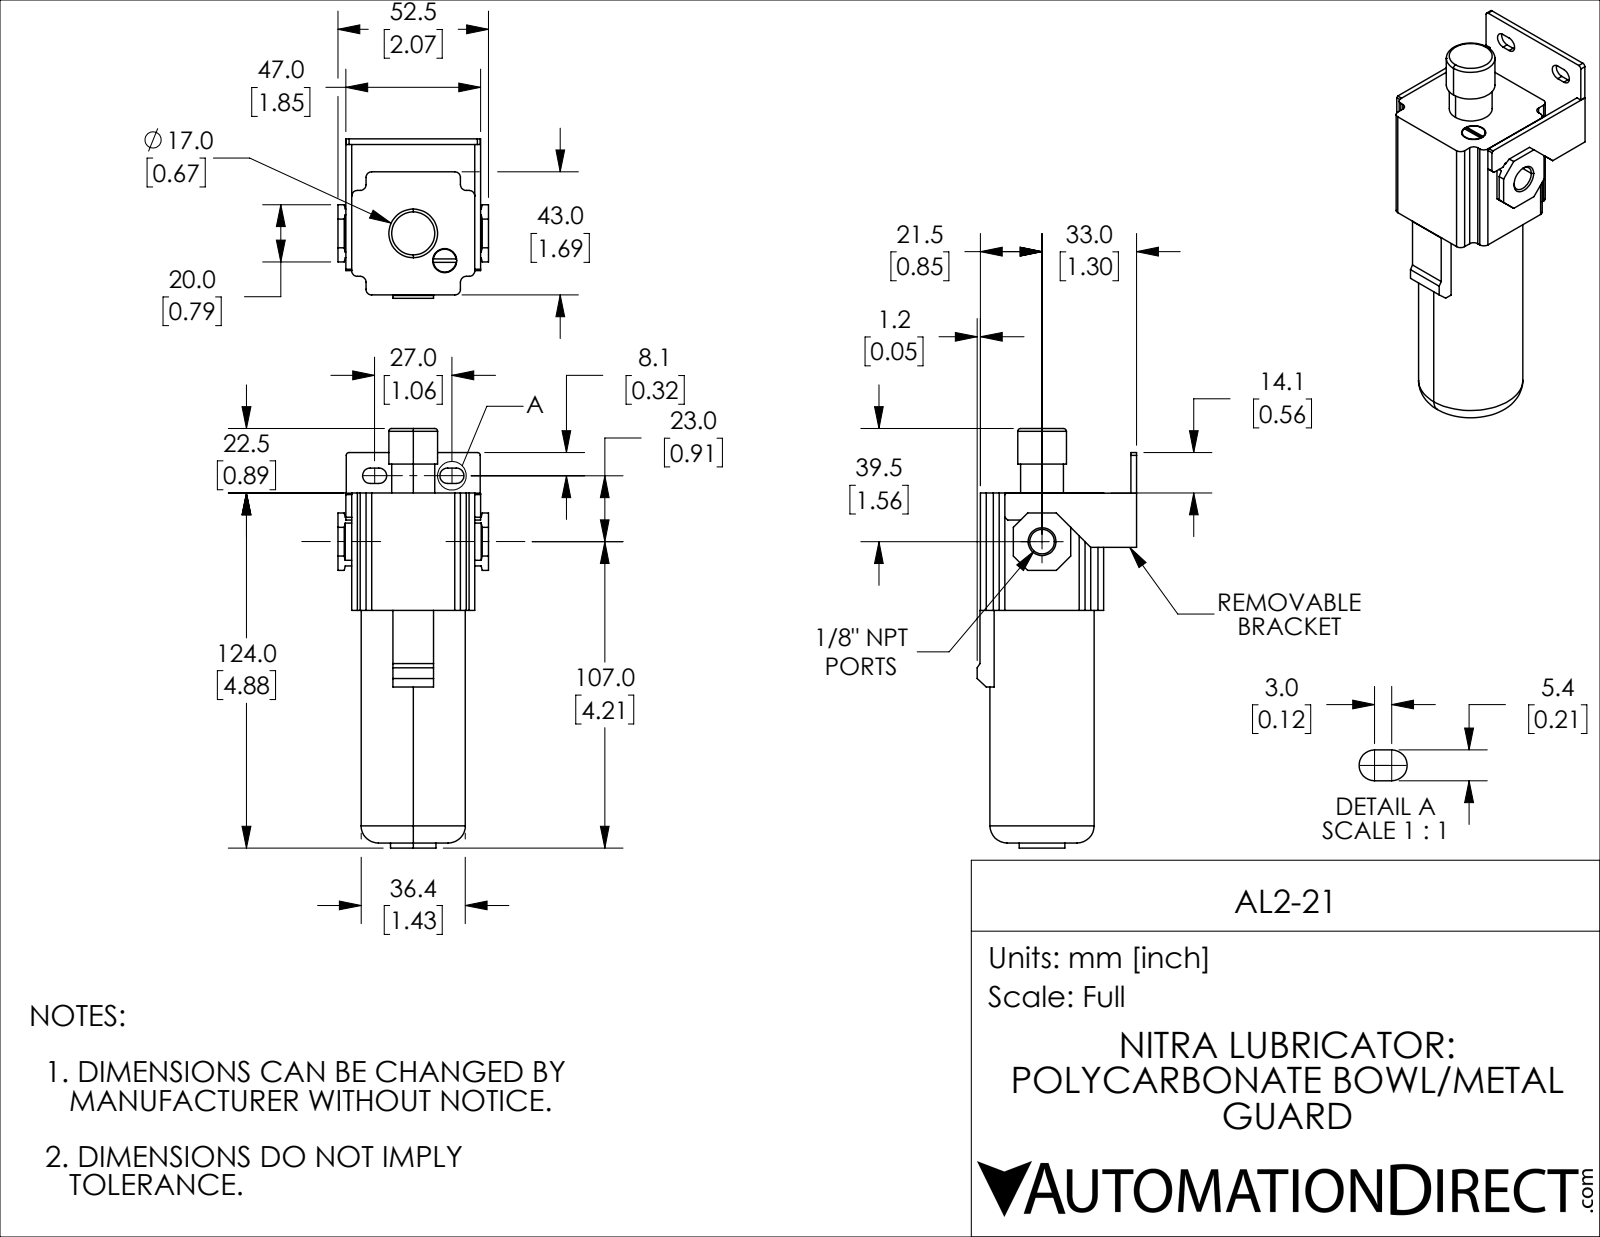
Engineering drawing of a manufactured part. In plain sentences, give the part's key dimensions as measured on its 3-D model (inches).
The part is named "AL2-21". Its 3-D file was written by "SolidWorks 2019 (CONFIG_CONTROL_DESIGN)". It is 1 solid with 137 faces: 95 planar, 34 cylindrical and 8 other. Overall it measures 5.768 by 2.192 by 2.067 inches. Its volume is 10.23 cubic inches and its surface area 41.67 square inches. Round holes: 1 of diameter 0.331, 1 of diameter 0.337. Round bosses or shafts: 1 of diameter 1.433, 1 of diameter 0.669, 1 of diameter 0.626, 1 of diameter 0.591, 1 of diameter 0.315. Partial cylindrical surfaces (rounded edges, fillets, slot ends): 12 of radius 0.079, 4 of radius 0.106, 2 of radius 0.039. The main face-to-face distances are 0.079, 1.693, 2.067, 0.453, 1.772, 0.374, 2.146, 1.614, 1.85, 0.108.
